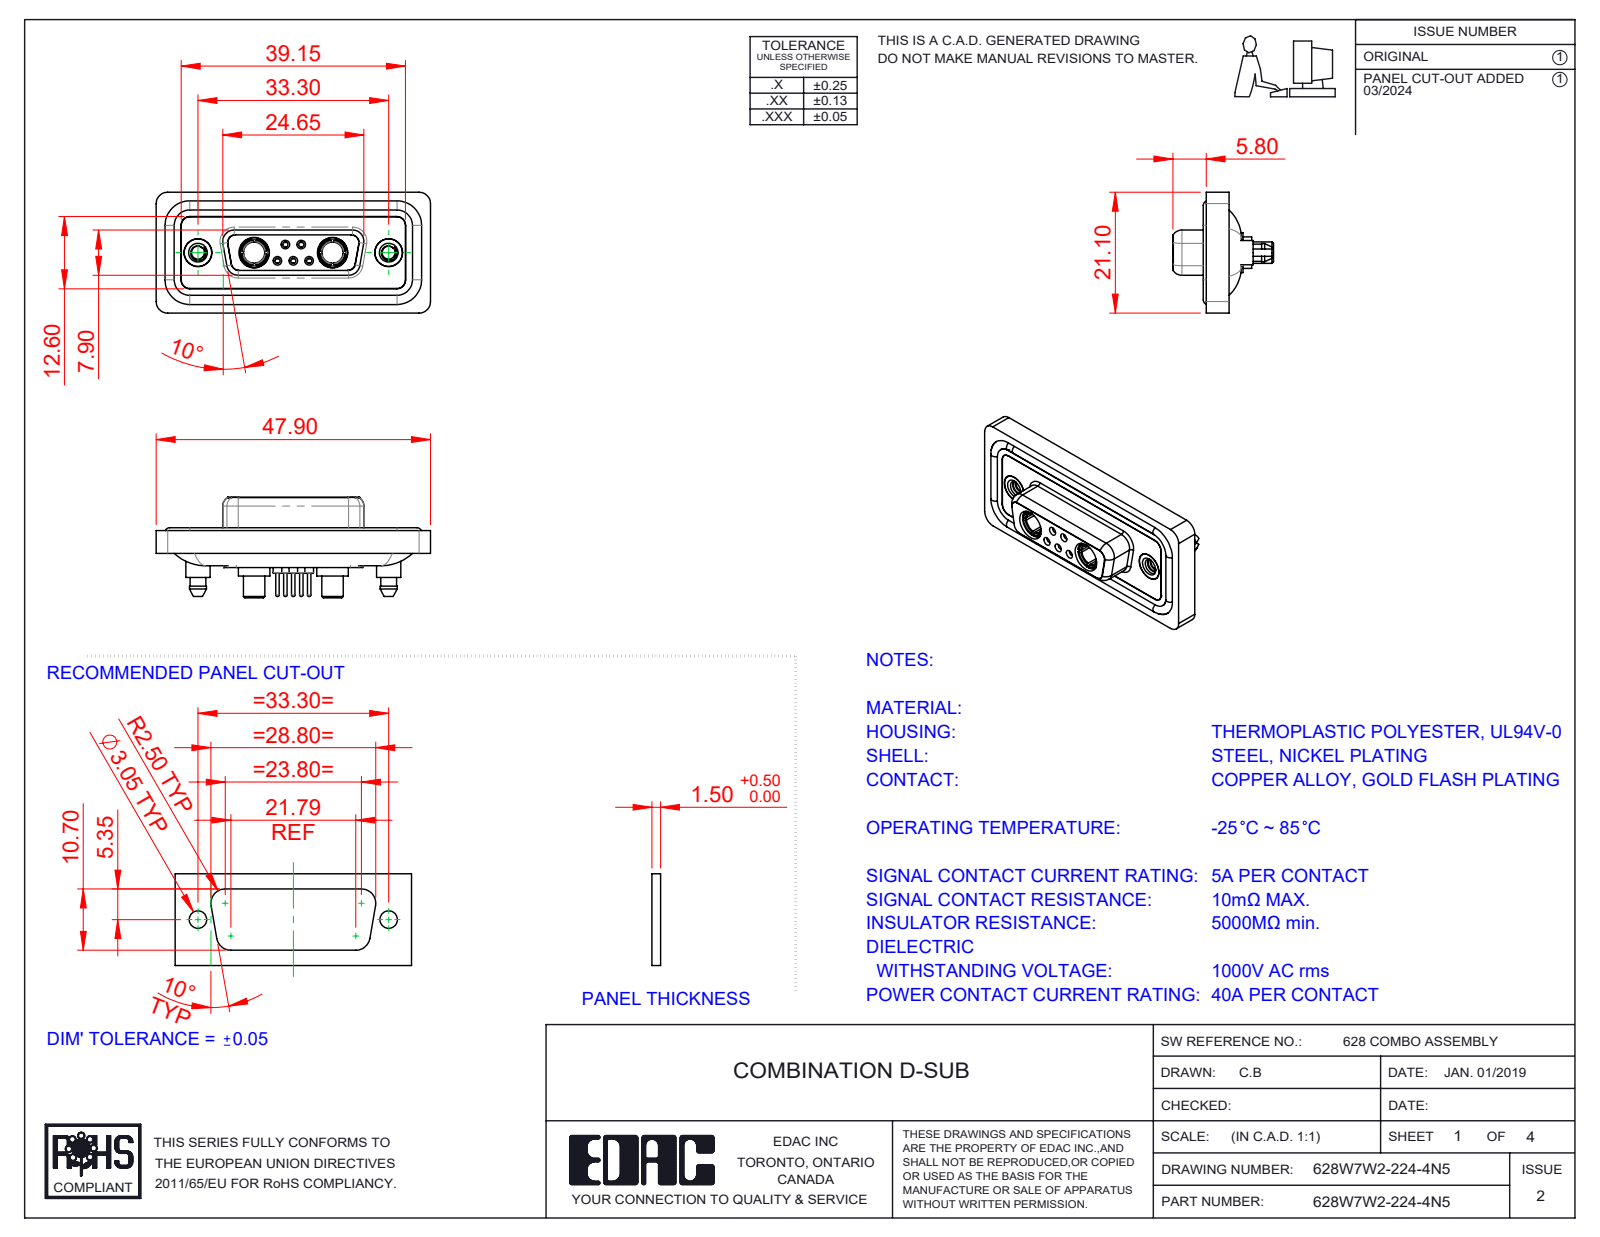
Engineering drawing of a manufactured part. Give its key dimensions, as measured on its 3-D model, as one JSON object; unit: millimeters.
{"part_name": "Power Socket_40A S; 628W7W2-224-4N5; 628Combo Waterproof Housing_15 Contacts; 628Combo Housing_7W2 (+5 more)", "step_written_by": "SolidWorks 2023 (CONFIG_CONTROL_DESIGN)", "units": "millimeters", "bodies": {"solids": 16, "faces": 859, "planar": 254, "cylindrical": 361, "other": 244}, "overall_size": [47.9, 21.1, 17.55], "volume_mm3": 6248, "surface_area_mm2": 10240, "round_holes": [[0.9, 5], [1.1, 5], [1.5, 5], [2, 5], [4.85, 4], [1.6, 3], [1.7, 2], [2.26, 2], [3.7, 2], [4, 2], [4.05, 2], [5, 2]], "round_bosses_or_shafts": [[1.6, 6], [2.2, 5], [0.6, 5], [5.5, 2], [5.4, 2], [5.2, 2], [4.96, 2], [4.95, 2]], "partial_cylinders_radius": [[1.5, 24], [2, 20], [1.35, 12], [1.6, 10], [0.25, 4], [0.5, 4], [0.6, 4], [0.65, 4]], "face_to_face_distances": [0.4, 1.8, 1.6, 0.5, 2.9, 1.1, 7.45, 5.65, 6.6, 7.05], "hole_center_spacings": [3.16, 2.77, 9.8, 23.5, 4.31, 4.33, 5.03, 5.04]}
